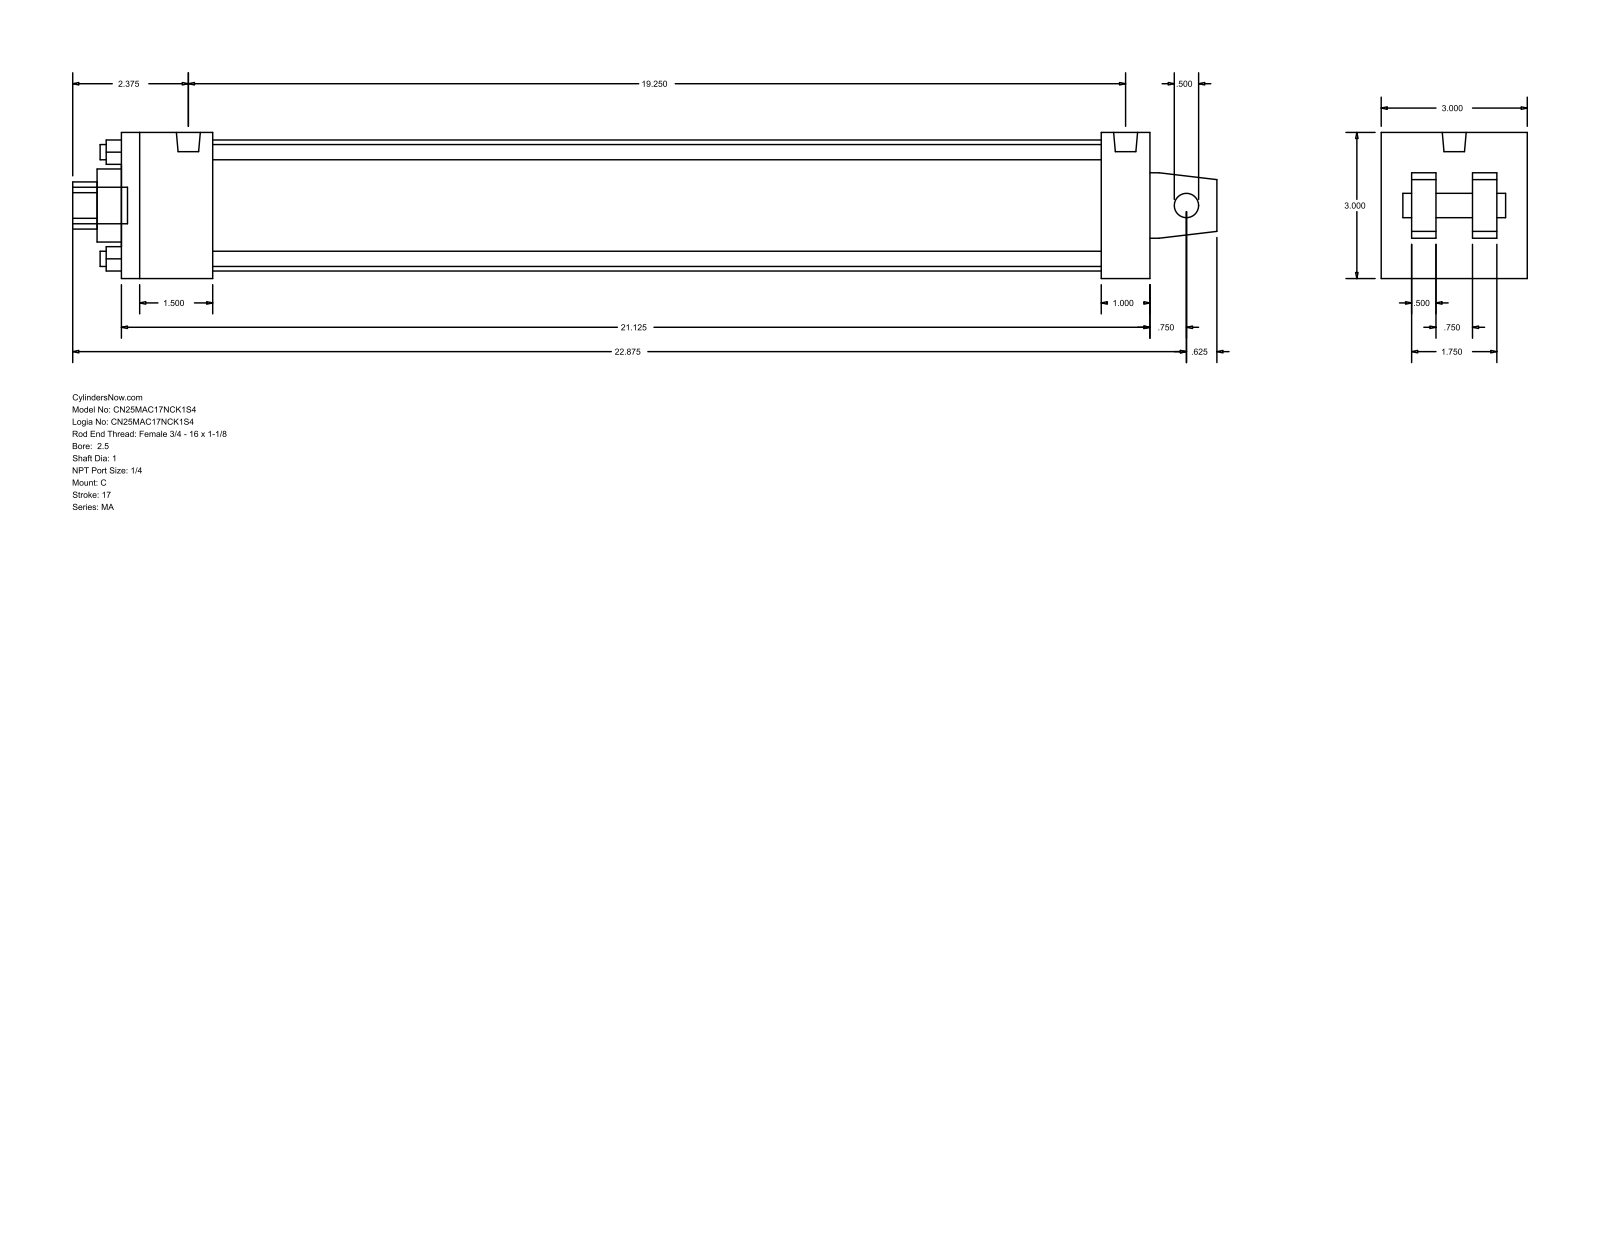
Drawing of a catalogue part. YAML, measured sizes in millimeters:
part_name: "MA_C__0250_1"
step_written_by: "GSSL Pune (CONFIG_CONTROL_DESIGN)"
units: millimeters
bodies: {solids: 0, faces: 103, planar: 76, cylindrical: 27, other: 0}
overall_size: [596.9, 76.2, 76.2]
round_holes:
  - {diameter: 7.94, count: 4}
  - {diameter: 12.7, count: 1}
  - {diameter: 25.4, count: 1}
  - {diameter: 38.1, count: 1}
  - {diameter: 68.33, count: 1}
round_bosses_or_shafts:
  - {diameter: 7.94, count: 4}
  - {diameter: 12.49, count: 2}
  - {diameter: 19.05, count: 1}
partial_cylinders:
  - {radius: 12.29, count: 1}
face_to_face_distances: [76.2, 536.58, 47.63, 12.7, 15.87, 60.33, 25.4, 28.57, 511.18, 463.55]
hole_center_spacings: [39.33, 55.62, 78.66]
